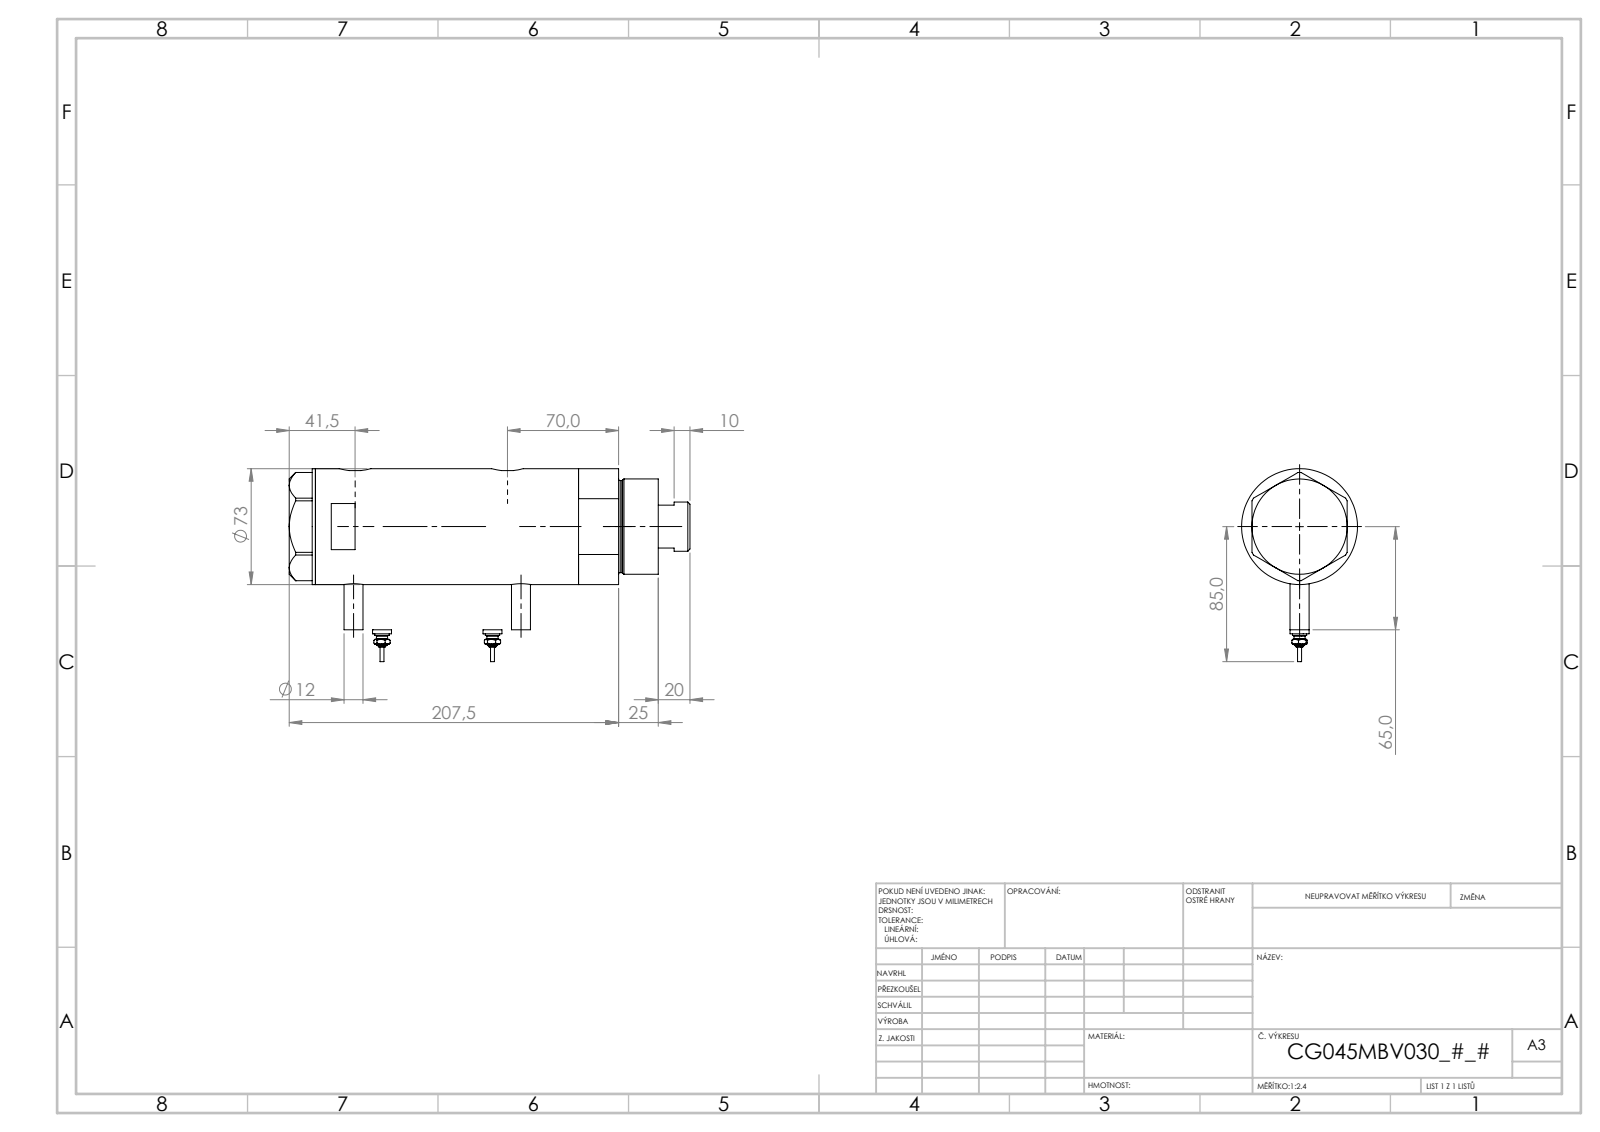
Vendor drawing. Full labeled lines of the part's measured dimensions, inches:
Part name (STEP PRODUCT): V270CG_VC; V270CG_BACK; V270CG_FRONT; V270CG_SWITCH (+1 more)
STEP written by: SolidWorks 2019 (CONFIG_CONTROL_DESIGN)
Units: inches
Bodies: 6 solids, 231 faces (78 planar, 79 cylindrical, 74 other)
Overall size (bounding box): 8.721 × 4.146 × 2.874
Volume: 47.09 in³ · Surface area: 210.8 in²
Round holes (diameter × count): ⌀0.197 ×2, ⌀0.492 ×2, ⌀0.518 ×2, ⌀0.413 ×1, ⌀1.26 ×1, ⌀1.319 ×1, ⌀1.772 ×1, ⌀1.89 ×1, ⌀2.52 ×1
Round bosses / shafts (diameter × count): ⌀0.472 ×3, ⌀0.354 ×2, ⌀0.276 ×2, ⌀0.171 ×2, ⌀0.094 ×2, ⌀2.874 ×1, ⌀2.362 ×1, ⌀2.283 ×1
Partial cylindrical surfaces — rounded edges, fillets, slot ends (radius × count): R0.394 ×2
Main face-to-face distances: 3.824, 0.65, 4.474, 7.284, 7.933, 3.459, 1.673, 1.024, 2.801, 6.26
Hole centre spacings: 3.215, 0.039, 0.039, 0.335, 0.335, 2.841, 2.88, 2.88
